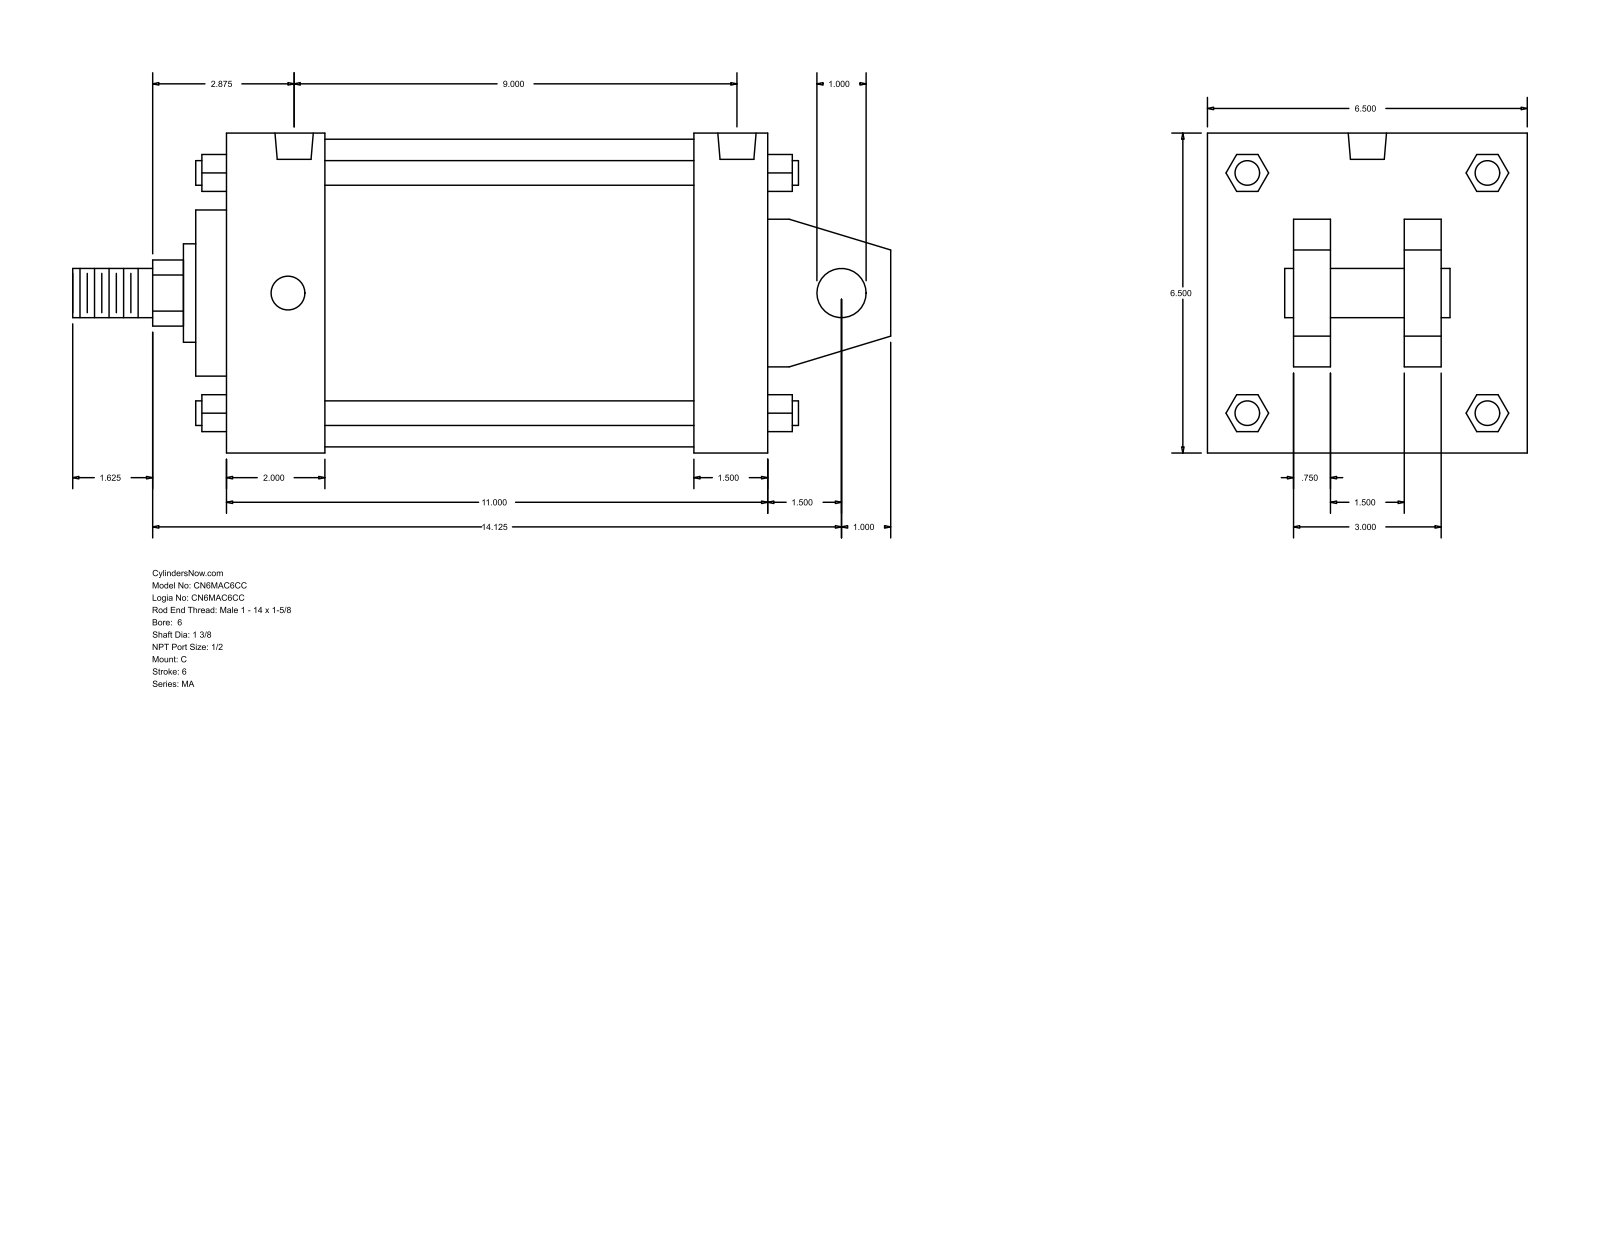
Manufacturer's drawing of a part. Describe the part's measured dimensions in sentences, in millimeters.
The part is named "MA_C__0600_1.375". Its 3-D file was written by "GSSL Pune (CONFIG_CONTROL_DESIGN)". It is 0 solids with 141 faces: 109 planar, 32 cylindrical and 0 other. Overall it measures 422.27 by 165.1 by 165.1 millimeters. Round holes: 4 of diameter 17.46, 2 of diameter 19.77. Round bosses or shafts: 4 of diameter 12.7, 2 of diameter 25.4, 1 of diameter 158.75, 1 of diameter 85.72, 1 of diameter 50.8, 1 of diameter 34.92. Partial cylindrical surfaces (rounded edges, fillets, slot ends): 1 of radius 17.06. The main face-to-face distances are 165.1, 279.4, 38.1, 19.05, 63.5, 101.6, 50.8, 120.65, 44.45, 241.3. The hole center spacings are 228.6, 3.17, 3.18, 225.42, 228.59, 231.77.
